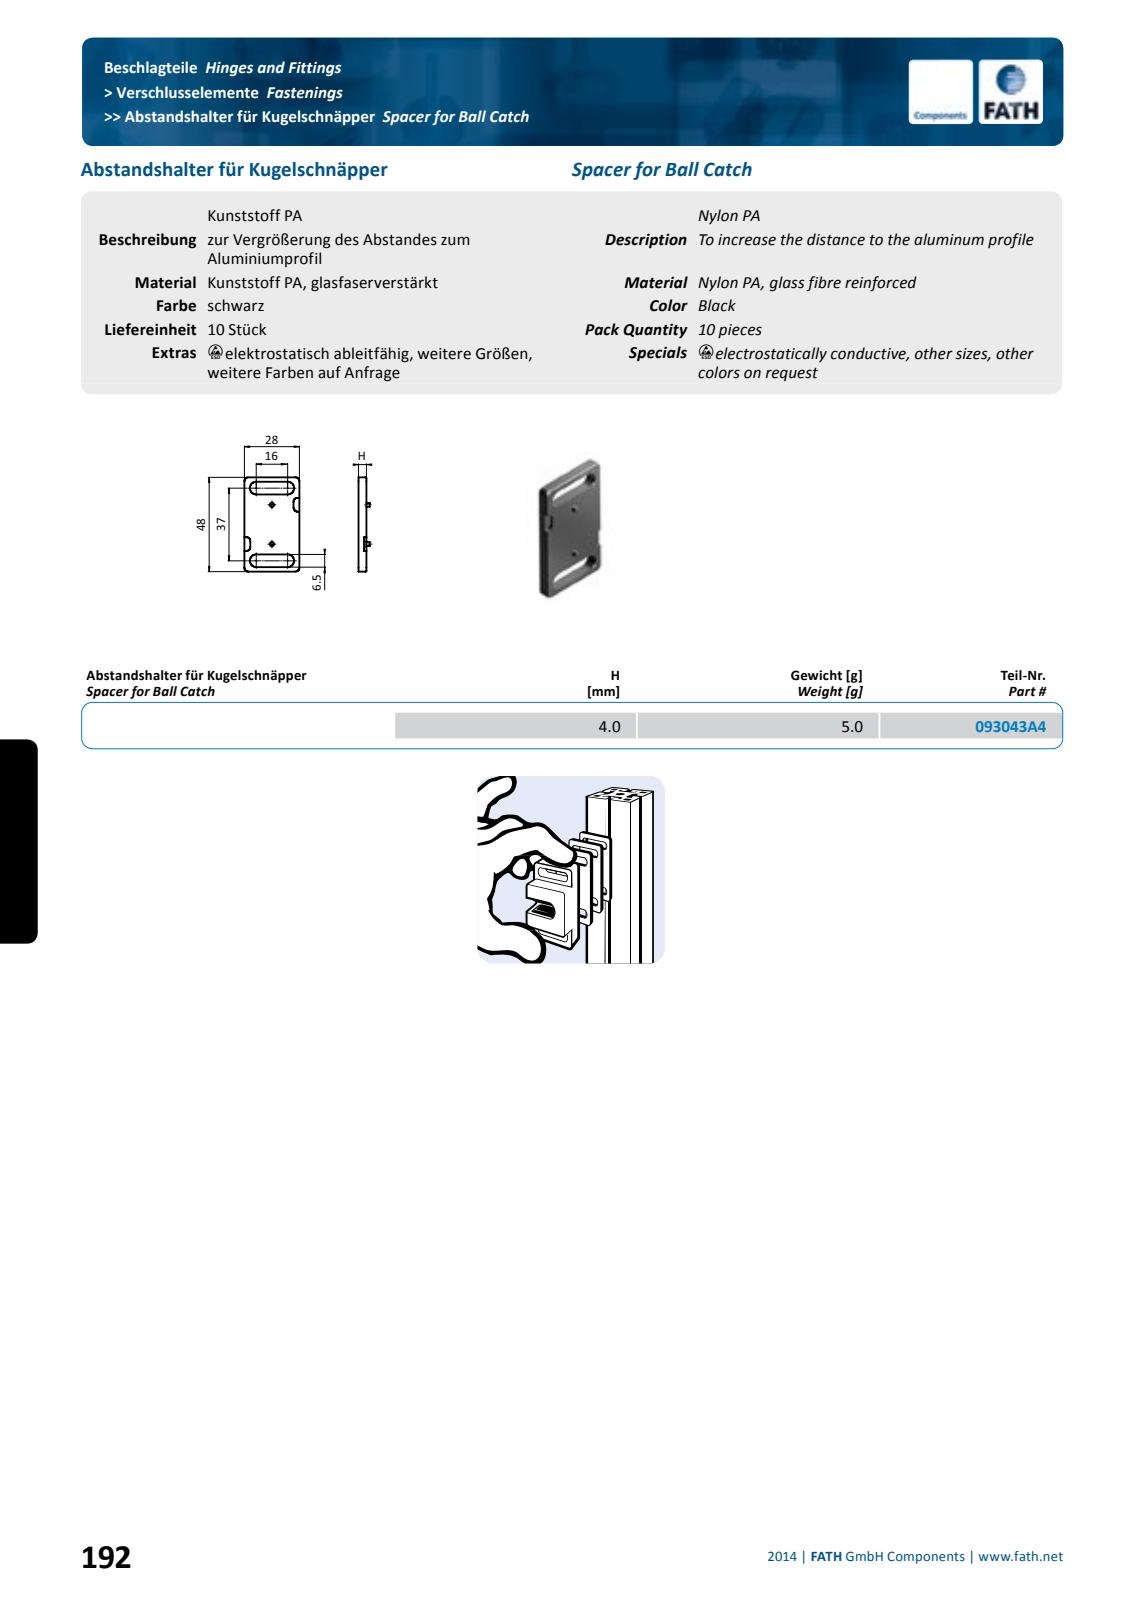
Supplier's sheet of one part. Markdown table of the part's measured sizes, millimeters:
| quantity | value |
| --- | --- |
| part name | fath_093043a4 |
| STEP written by | Spatial InterOp 3D (automotive_design) |
| units | millimeters |
| bodies | 1 solid, 68 faces (22 planar, 30 cylindrical, 16 other) |
| overall size | 48 × 28 × 5.7 |
| volume | 4 206 mm³ |
| surface area | 3 175 mm² |
| round holes (diameter × count) | 1.95 × 2 |
| round bosses / shafts (diameter × count) | 2 × 2 |
| partial cylindrical surfaces (radius × count) | 2 × 8, 0.5 × 4, 3.25 × 4 |
| main face-to-face distances | 4, 28, 8.75, 2.25, 39.25, 45.75, 37, 6.5, 48, 30.5 |
| hole center spacings | 20 |
